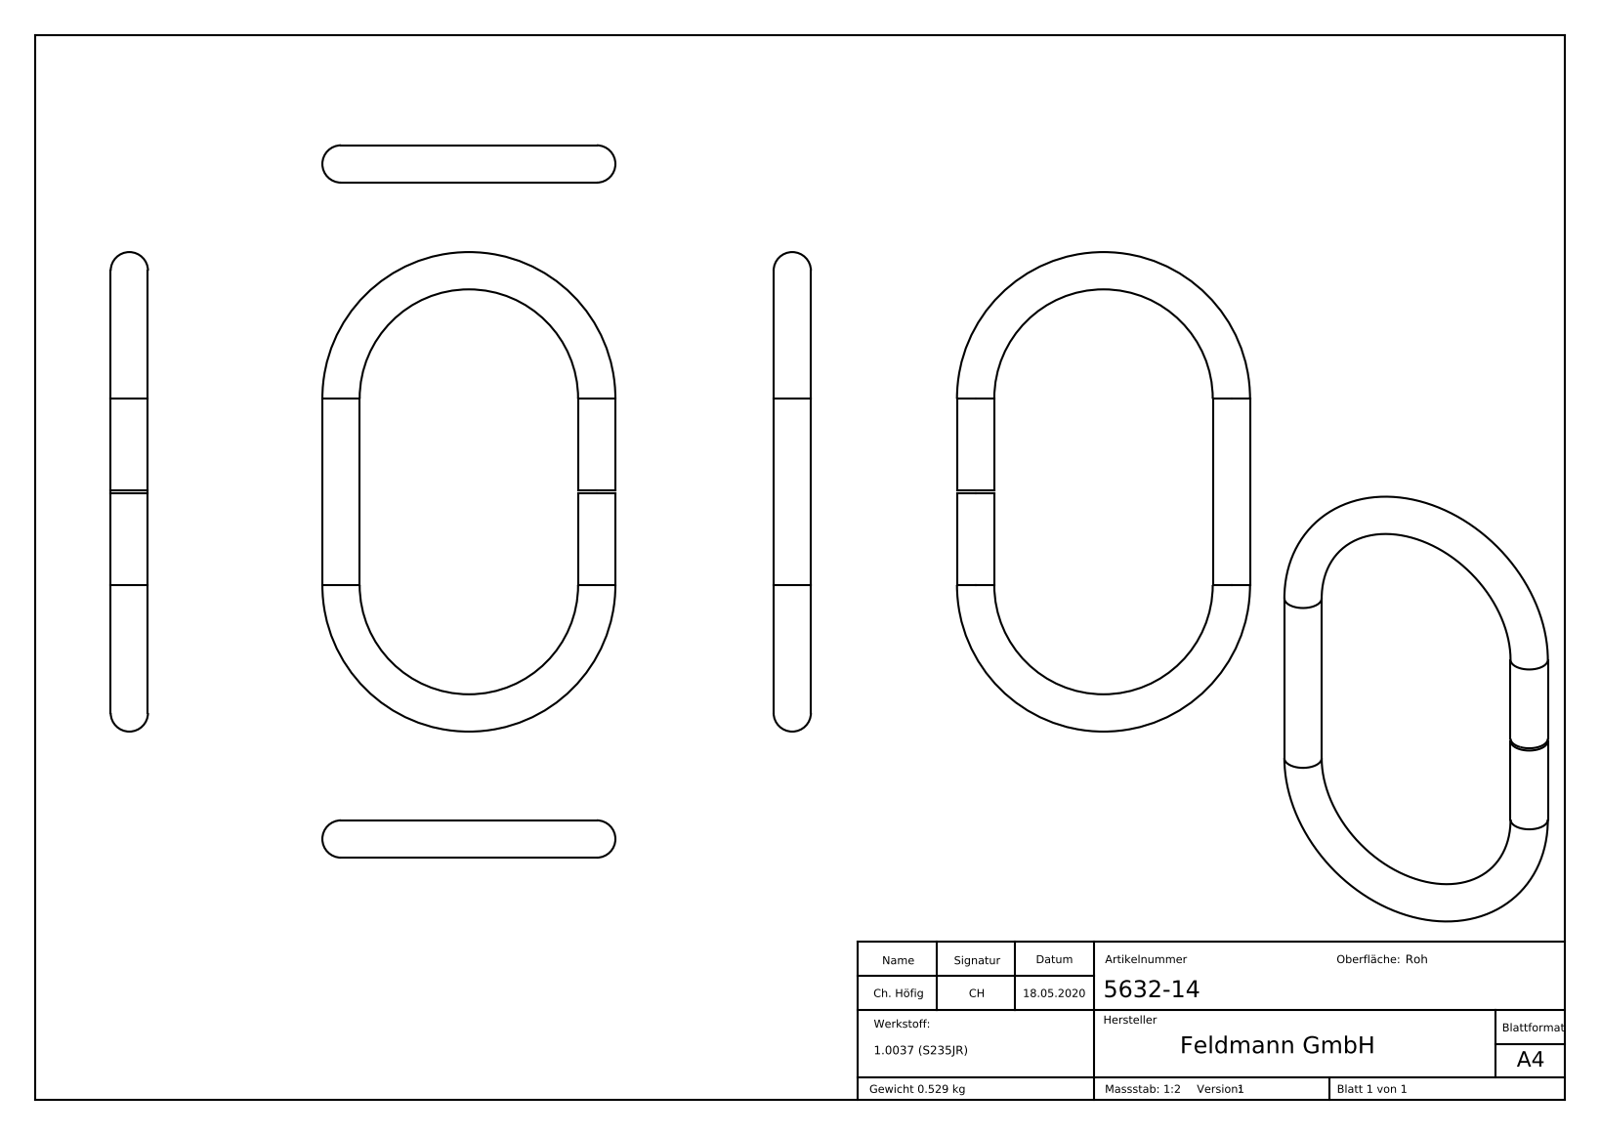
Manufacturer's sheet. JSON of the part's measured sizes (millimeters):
{"part_name": "5632-14", "step_written_by": "SolidWorks 2015 (CONFIG_CONTROL_DESIGN)", "units": "millimeters", "bodies": {"solids": 1, "faces": 207, "planar": 117, "cylindrical": 3, "other": 87}, "overall_size": [180, 110, 14], "volume_mm3": 67824, "surface_area_mm2": 19691, "round_bosses_or_shafts": [[14, 2]], "face_to_face_distances": [1, 1.1, 1.78, 0.34, 0.83, 0.74, 0.99, 2.43, 0.79, 1.21]}
